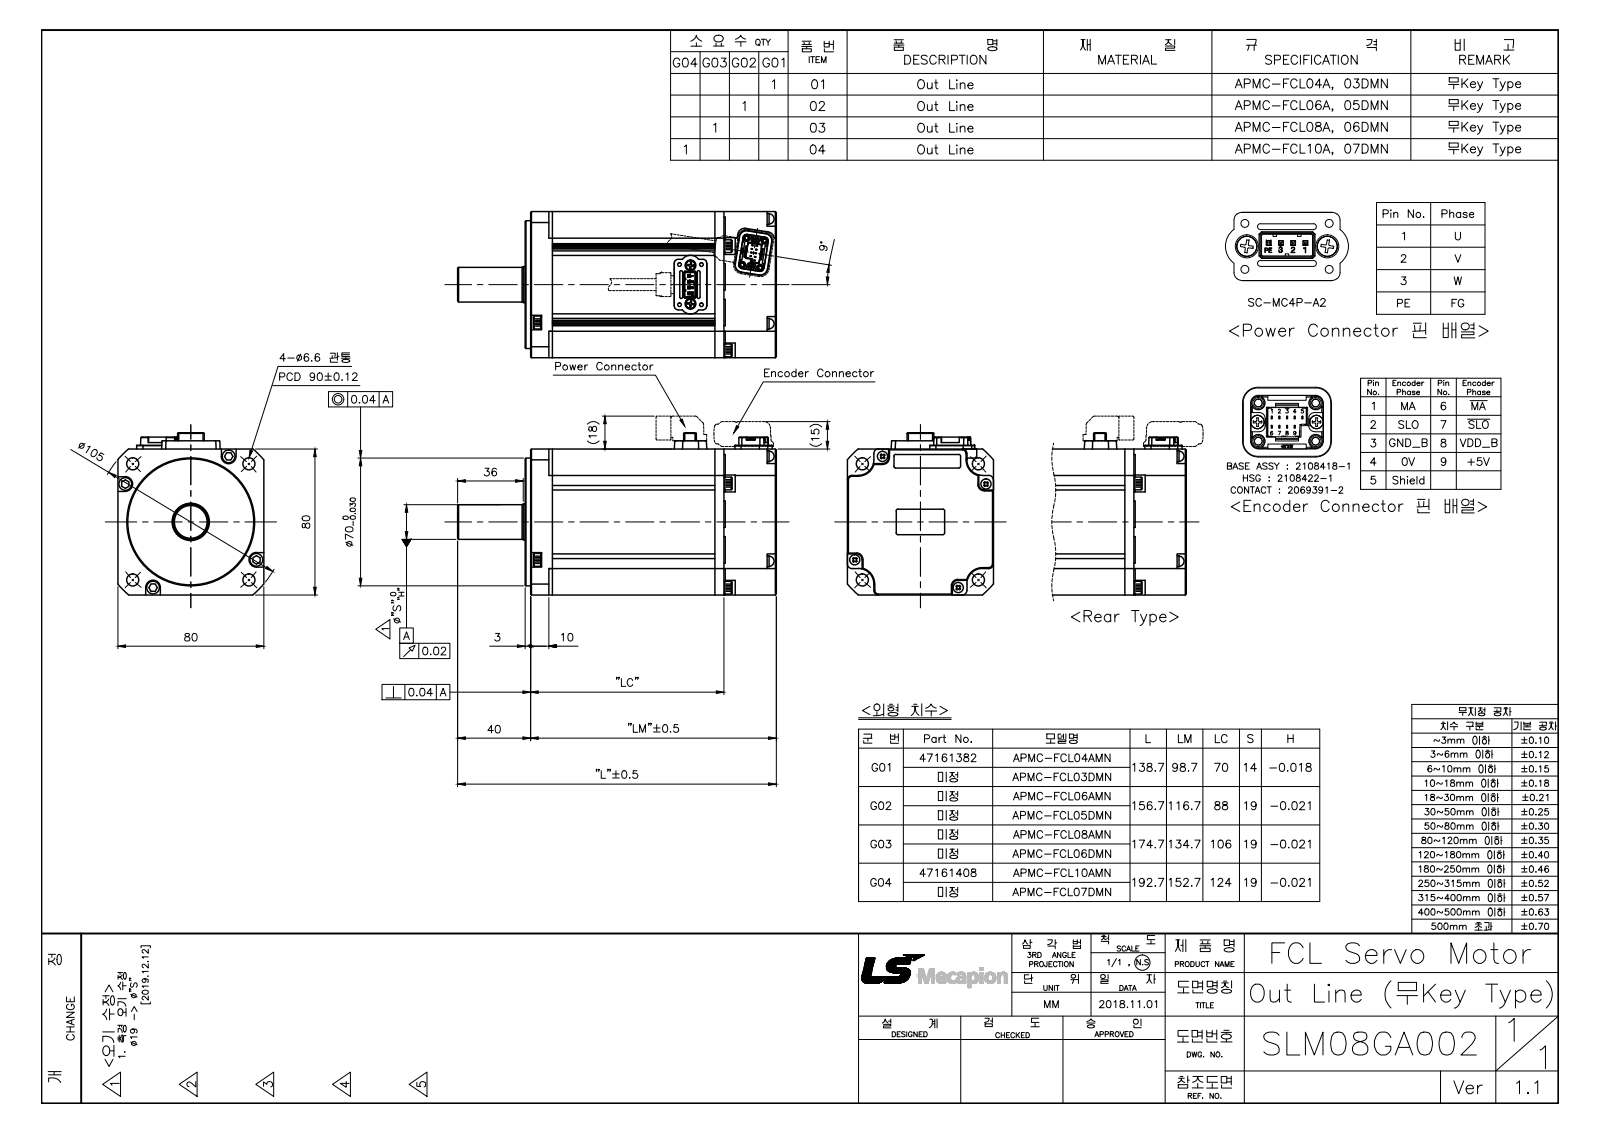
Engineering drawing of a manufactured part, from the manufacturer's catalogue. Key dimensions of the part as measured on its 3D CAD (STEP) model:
Part name (STEP PRODUCT): APMC-FCL04AMN, FCL03DMN
STEP written by: SolidWorks 2011 (AUTOMOTIVE_DESIGN)
Units: millimetres
Bodies: 44 solids, 1836 faces (1182 planar, 466 cylindrical, 188 other)
Overall size (bounding box): 138.7 × 88.7 × 80
Volume: 575 803 mm³ · Surface area: 105 604 mm²
Round holes (diameter × count): ⌀2.1 ×10, ⌀4 ×8, ⌀4.5 ×8, ⌀3 ×6, ⌀3.5 ×4, ⌀6.6 ×4, ⌀2 ×2, ⌀6 ×2, ⌀3.3 ×1, ⌀3.4 ×1, ⌀20.5 ×1
Round bosses / shafts (diameter × count): ⌀7.2 ×8, ⌀7 ×8, ⌀5.4 ×6, ⌀2.2 ×2, ⌀70 ×1, ⌀19.8 ×1, ⌀14 ×1
Partial cylindrical surfaces — rounded edges, fillets, slot ends (radius × count): R0.3 ×36, R0.2 ×20, R0.15 ×9, R2.5 ×9, R1 ×8, R2 ×8, R0.45 ×7, R0.11 ×6
Main face-to-face distances: 5, 53, 58, 0.7, 5.7, 58.7, 80, 28, 28.7, 33.7
Hole centre spacings: 41.5, 11.81, 52.73, 58.69, 68.66, 85.76, 6.02, 16.01
